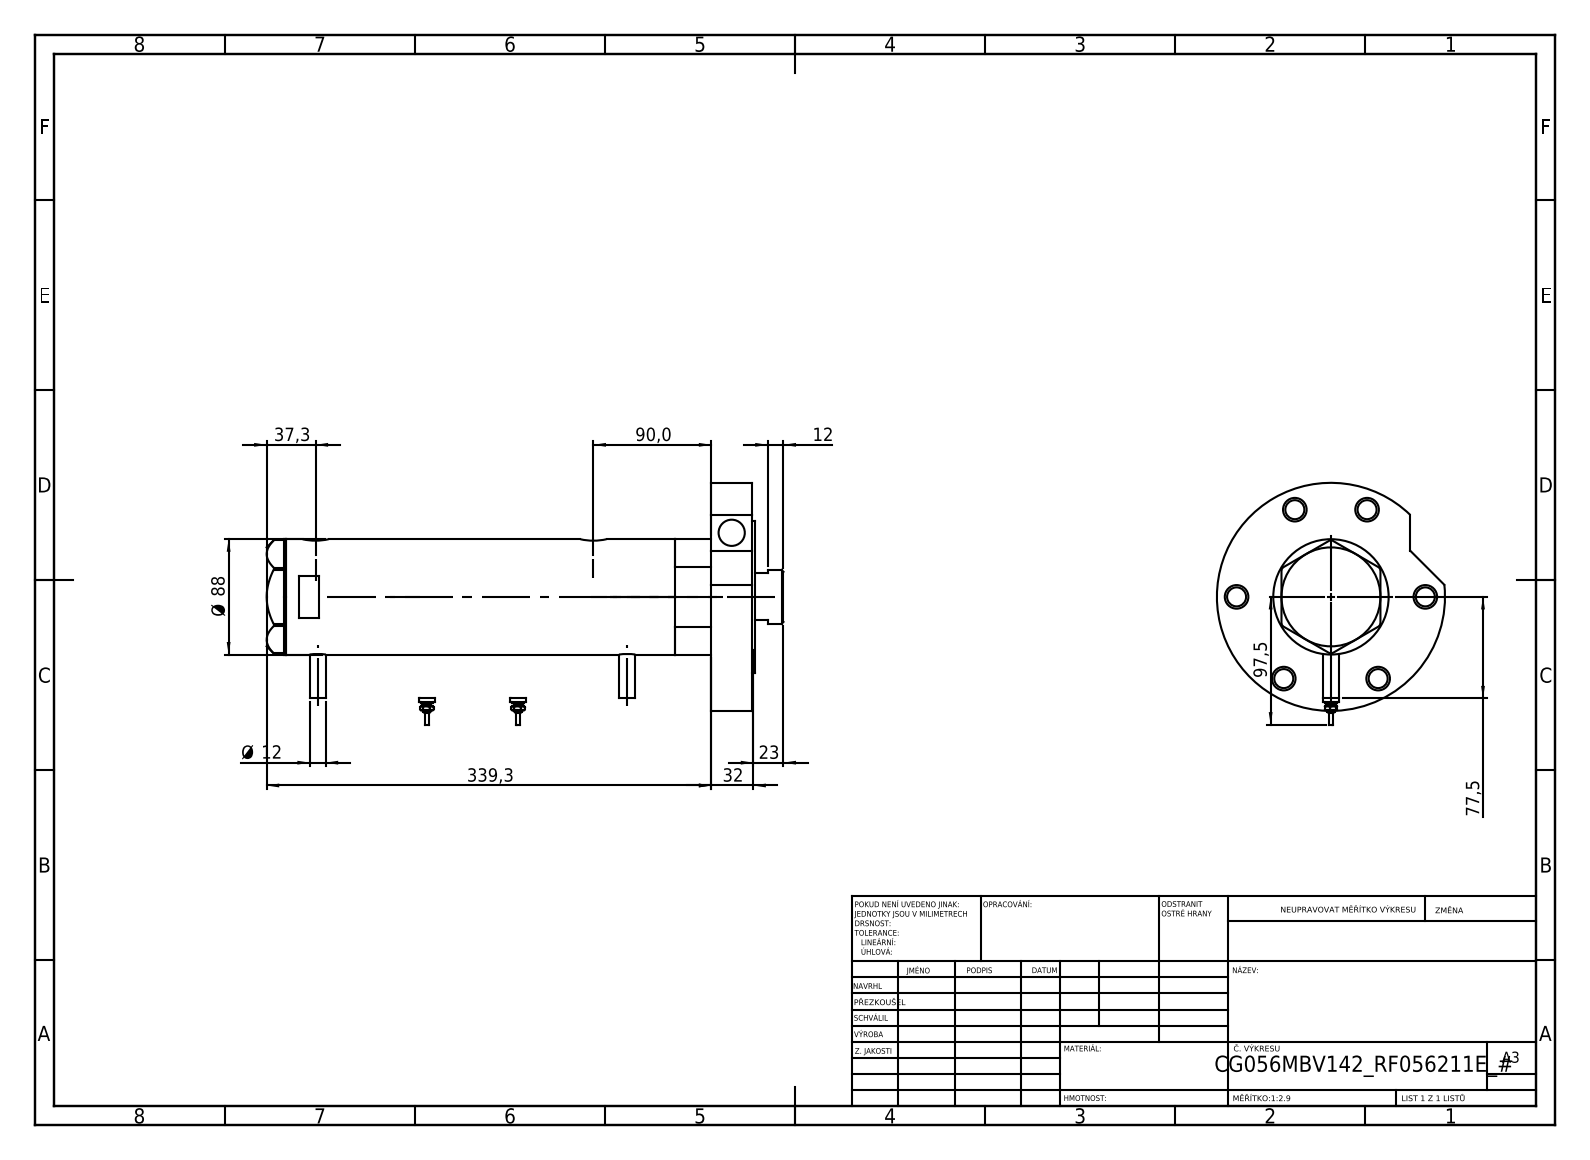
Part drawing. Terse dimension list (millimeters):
name: V270CG_FRONT; V270CG_VC; V270CG_BACK; V270CG_RF211E (+2 more)
written by: SolidWorks 2019 (CONFIG_CONTROL_DESIGN)
unit: mm
bodies: 7 solids, 257 faces (91 planar, 102 cylindrical, 64 other)
size: 394.3 × 184.5 × 174
volume: 2 570 000 mm³; area: 361 043 mm²
holes: 7× ⌀14.5, 6× ⌀18, 3× ⌀20, 2× ⌀12.5, 2× ⌀13.16, 1× ⌀42, 1× ⌀43.5, 1× ⌀56, 1× ⌀60, 1× ⌀75, 1× ⌀80
bosses: 4× ⌀12, 2× ⌀9, 2× ⌀7, 2× ⌀4.5, 2× ⌀2.5, 1× ⌀174, 1× ⌀116, 1× ⌀88
face distances: 31, 2, 357.3, 324.3, 355.3, 33, 234.4, 89.9, 120.9, 122.9
hole spacings: 72, 80, 119.73, 124.71, 129.15, 143.69, 1.7, 25.8
